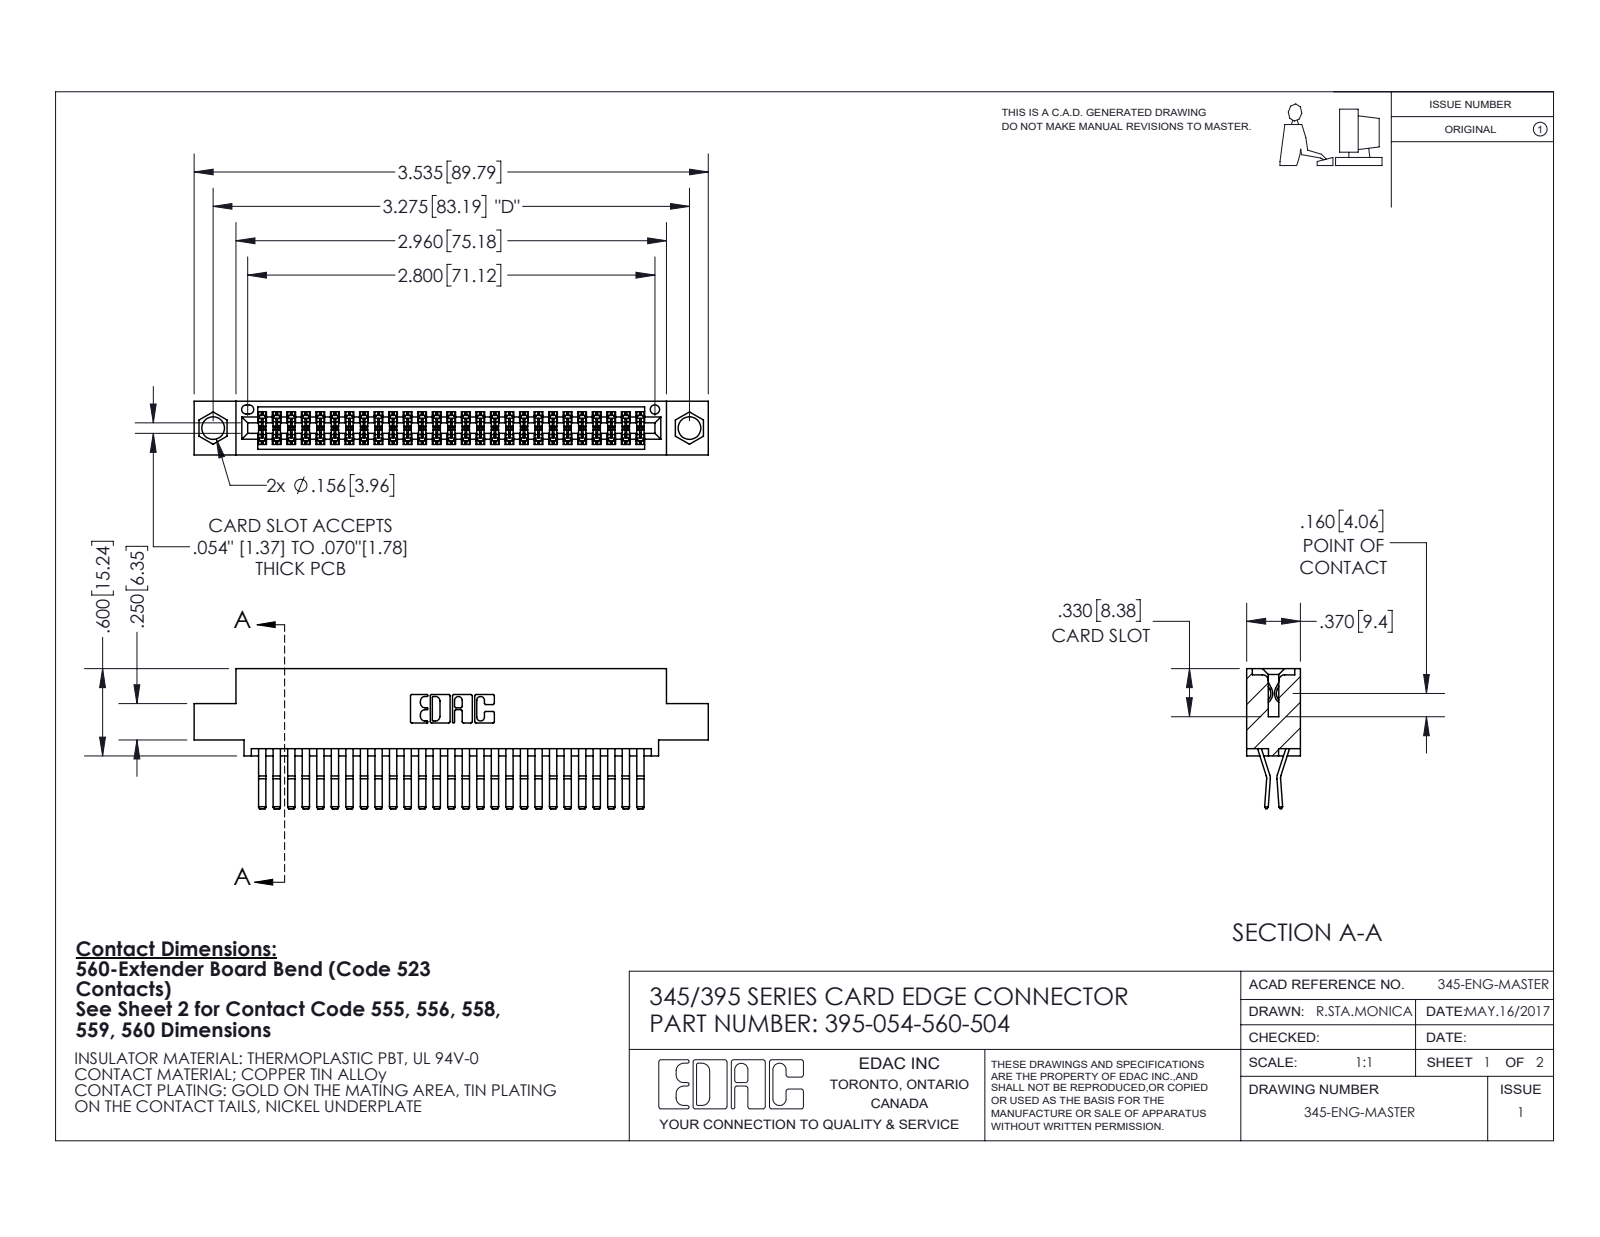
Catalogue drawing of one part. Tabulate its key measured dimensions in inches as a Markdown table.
| quantity | value |
| --- | --- |
| part name | 395-054-560-504; 345-292-001_560 Tail; 345 Part_0.110 Offset - 0.156 Dia-TI |
| STEP written by | SolidWorks 2020 (CONFIG_CONTROL_DESIGN) |
| units | inches |
| bodies | 55 solids, 2952 faces (1880 planar, 1072 cylindrical, 0 other) |
| overall size | 3.535 × 0.962 × 0.37 |
| volume | 0.534 in³ |
| surface area | 20.94 in² |
| round holes (diameter × count) | 0.156 × 2, 0.064 × 1 |
| partial cylindrical surfaces (radius × count) | 0.006 × 81, 0.01 × 22, 0.007 × 6, 0.031 × 6, 0.026 × 3, 0.01 × 2, 0.014 × 2, 0.019 × 2 |
| main face-to-face distances | 0.025, 0.298, 0.072, 0.37, 0.2, 0.098, 0.272, 0.225, 0.175, 0.149 |
| hole center spacings | 0.27, 3.04, 3.275 |
